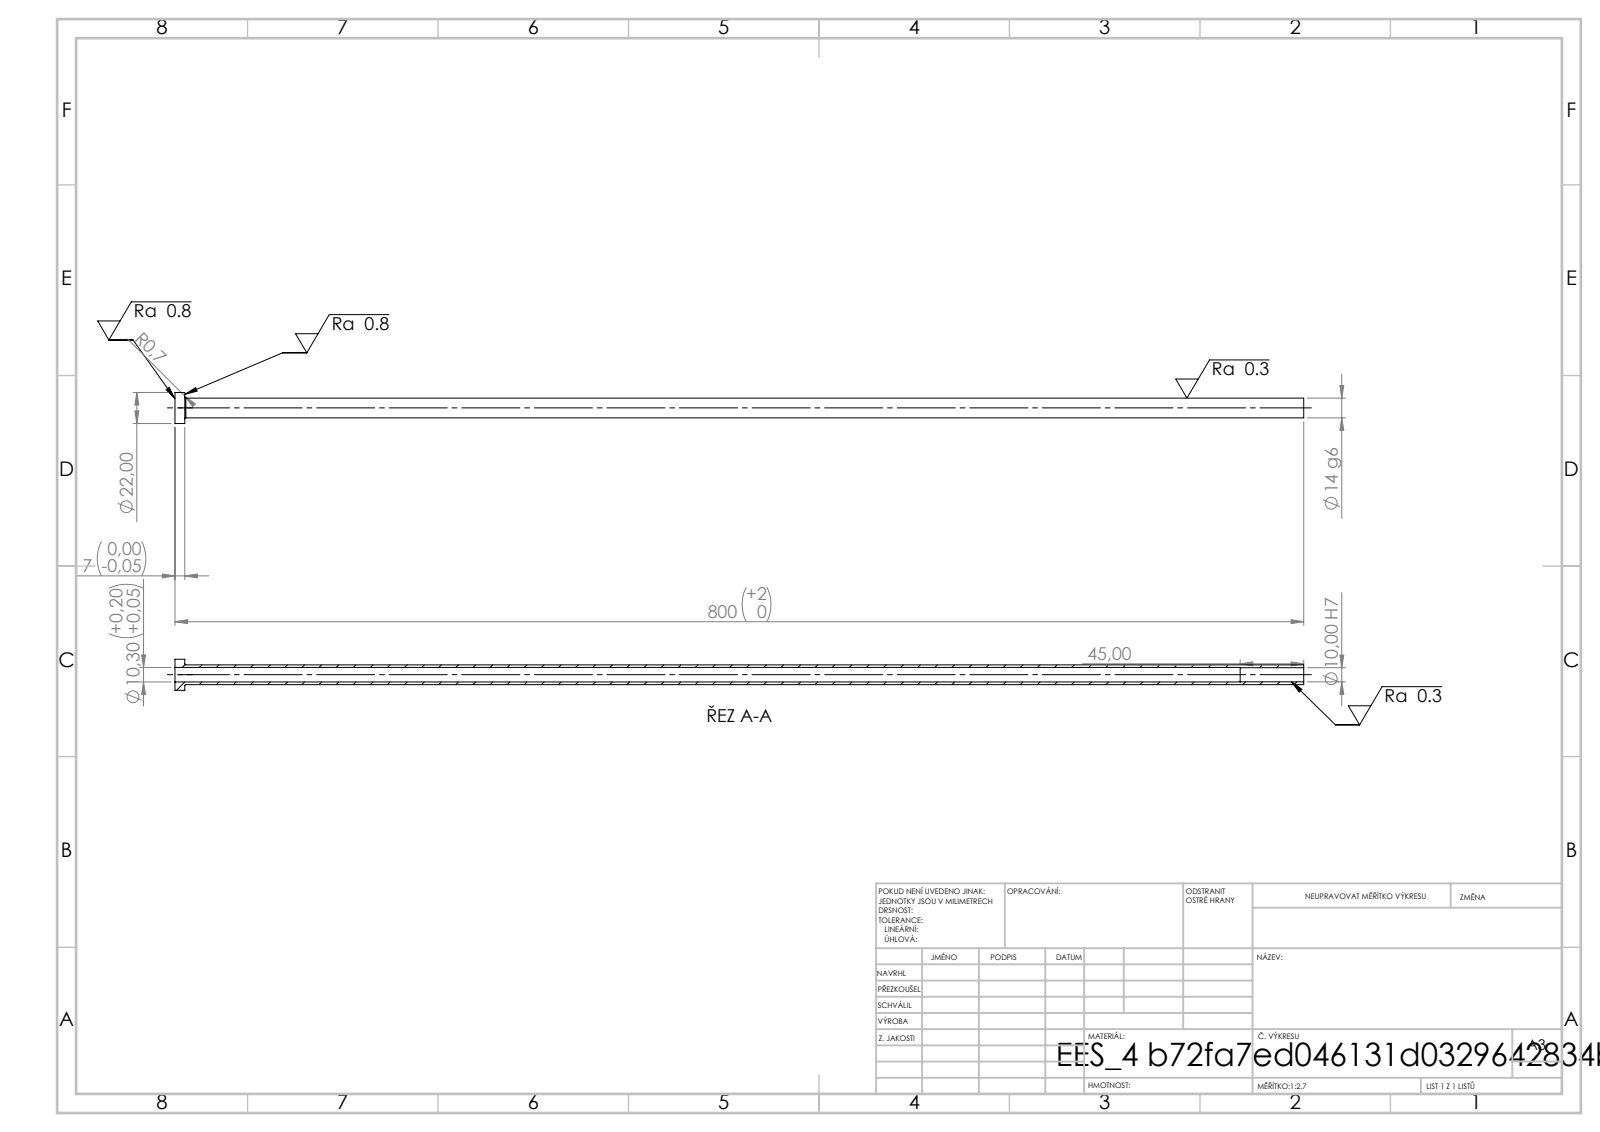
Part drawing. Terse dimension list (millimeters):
written by: SolidWorks 2019 (CONFIG_CONTROL_DESIGN)
unit: mm
bodies: 1 solid, 14 faces (4 planar, 8 cylindrical, 2 other)
size: 800 × 22 × 22
volume: 58 295 mm³; area: 61 796 mm²
holes: 1× ⌀10, 1× ⌀10.3
bosses: 1× ⌀22, 1× ⌀14
face distances: 7, 800, 793, 755, 748, 45
